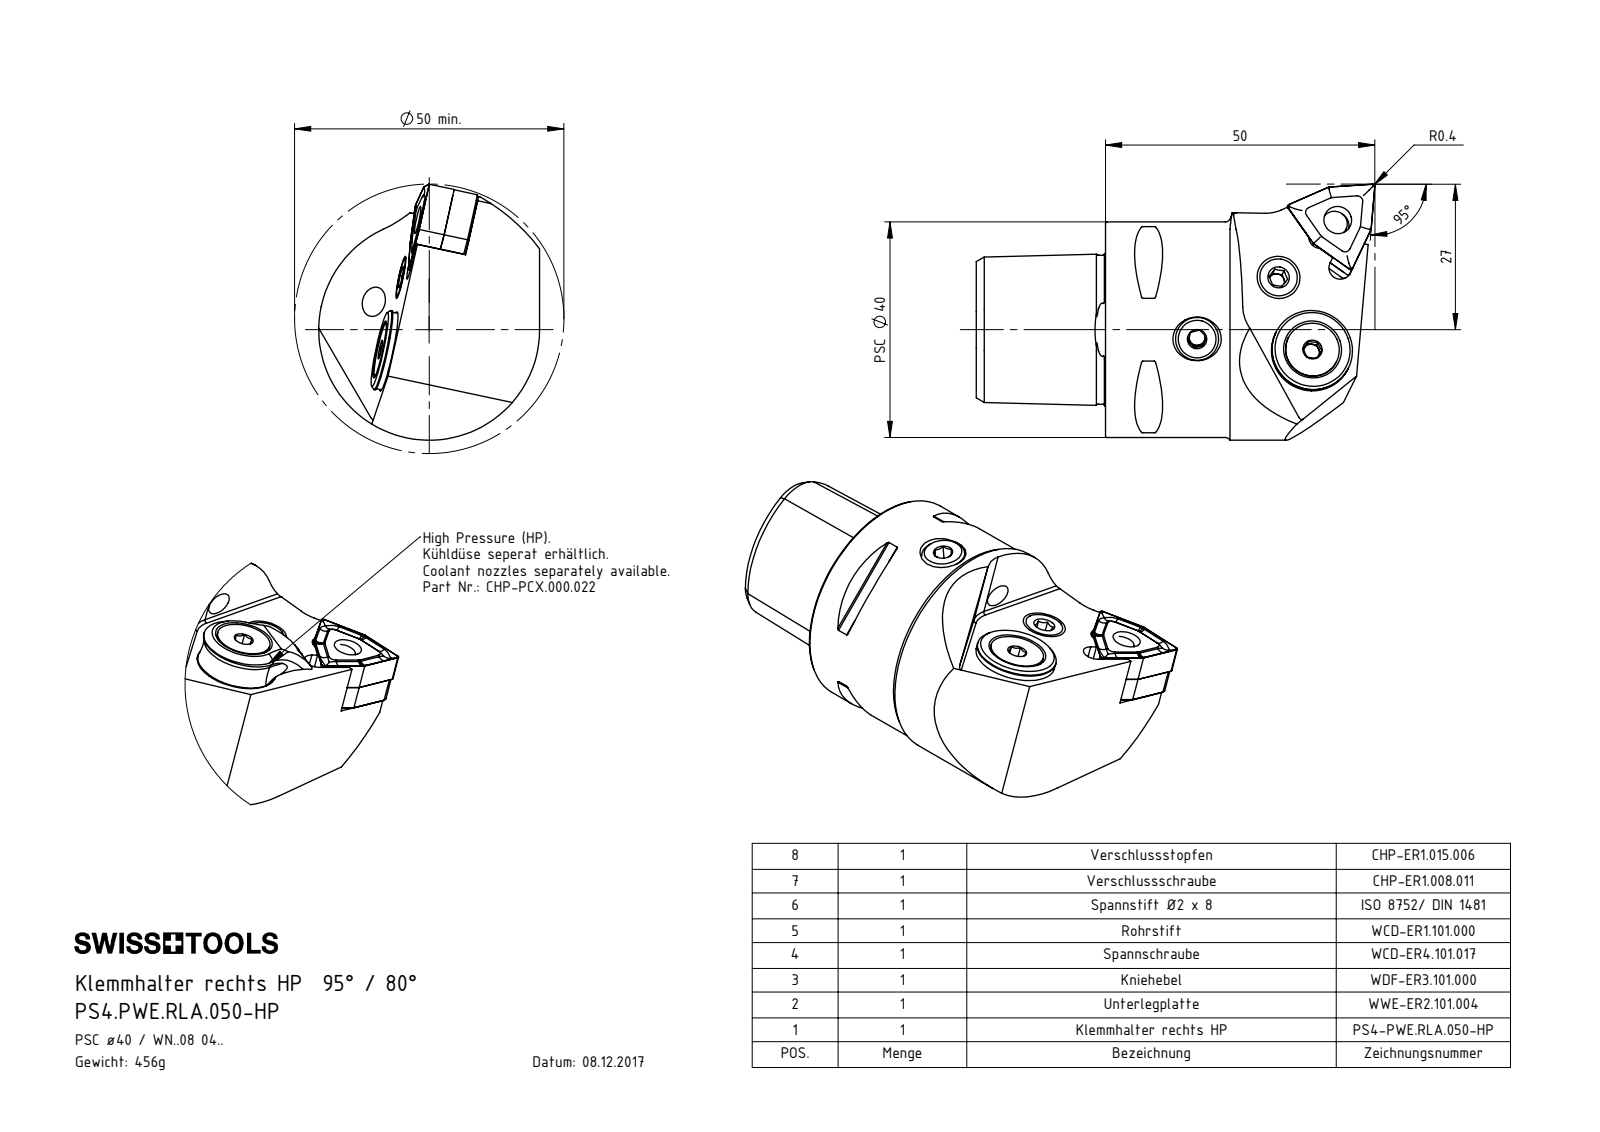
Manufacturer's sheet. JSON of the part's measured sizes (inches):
{"part_name": "DIN 3771 - 13x1; DIN 7991 - M5x15; CHP-ER1.015.006_A; PS4.PWE.RLA.050-HP (+8 more)", "step_written_by": "SolidWorks 2017 (AUTOMOTIVE_DESIGN)", "units": "inches", "bodies": {"solids": 11, "faces": 353, "planar": 142, "cylindrical": 71, "other": 140}, "overall_size": [2.914, 1.861, 1.594], "volume_in3": 3.411, "surface_area_in2": 28.69, "round_holes": [[0.165, 3], [0.276, 2], [0.047, 1], [0.079, 1], [0.098, 1], [0.118, 1], [0.157, 1], [0.181, 1], [0.197, 1], [0.203, 1], [0.205, 1], [0.264, 1]], "round_bosses_or_shafts": [[0.315, 2], [1.575, 1], [0.591, 1], [0.528, 1], [0.394, 1], [0.311, 1], [0.252, 1], [0.217, 1]], "partial_cylinders_radius": [[0.012, 8], [0.016, 3], [0.039, 3], [0.098, 3], [0.031, 2], [0.083, 1], [0.091, 1], [0.093, 1]], "face_to_face_distances": [0.187, 0.177, 0.611, 0.188, 0.945, 0.176, 0.176, 0.187, 0.186, 0.363], "hole_center_spacings": [0.178, 0.178, 0.481, 0.483, 0.525, 0.526, 0.614, 0.74]}
